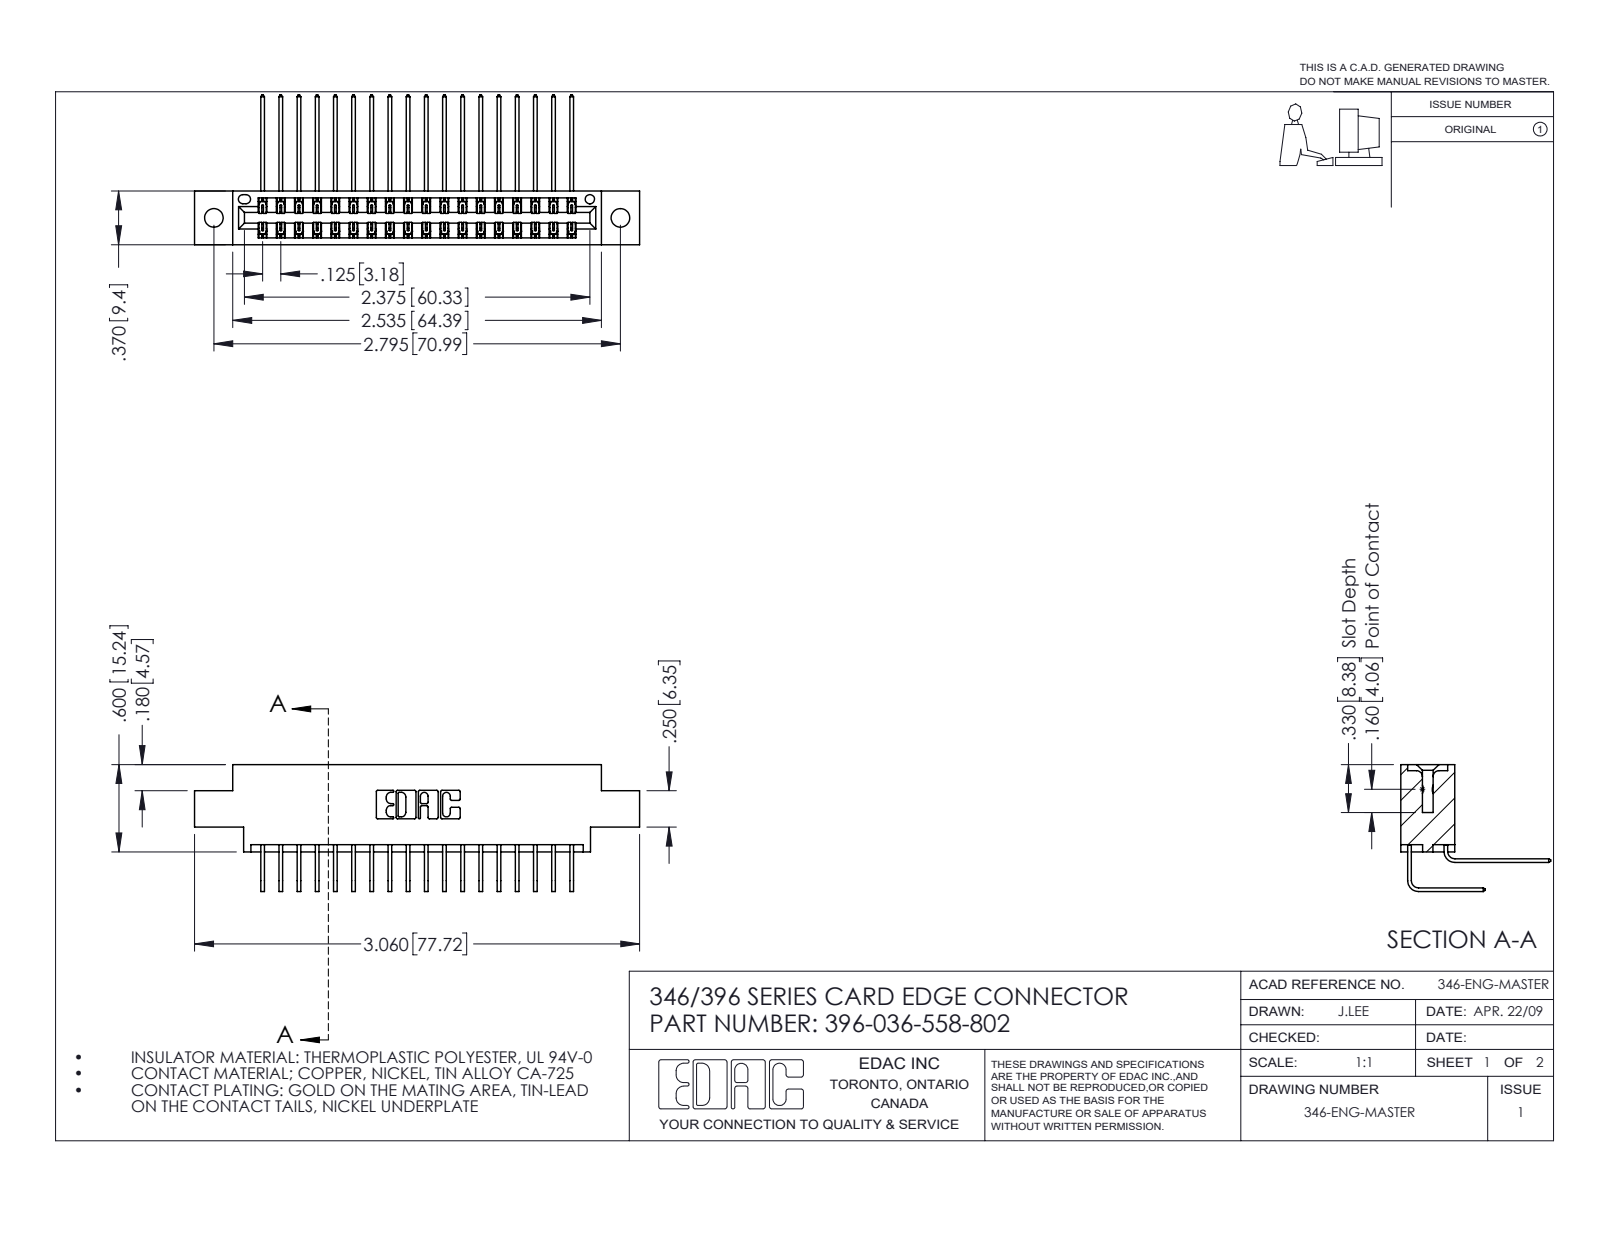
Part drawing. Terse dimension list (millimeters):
name: 346 Part_0.170 Offset - 0.128 Dia; 396-036-558-802; 345-292-001_558 559 Tail - 1; 345-292-001_558 Tail - 2
written by: SolidWorks 2016 (CONFIG_CONTROL_DESIGN)
unit: mm
bodies: 37 solids, 2070 faces (1412 planar, 658 cylindrical, 0 other)
size: 77.7 × 26.2 × 22.2
volume: 7 410 mm³; area: 10 720 mm²
holes: 2× ⌀3.3, 1× ⌀1.6
rounds: 54× R0.2, 22× R0.3, 6× R0.2, 6× R0.8, 3× R0.7, 2× R0.4, 2× R0.6, 2× R0.6
face distances: 8.2, 1.2, 9.4, 6.4, 0.6, 7.6, 1.8, 7, 3.8, 5.6
hole spacings: 6.2, 65.7, 71
